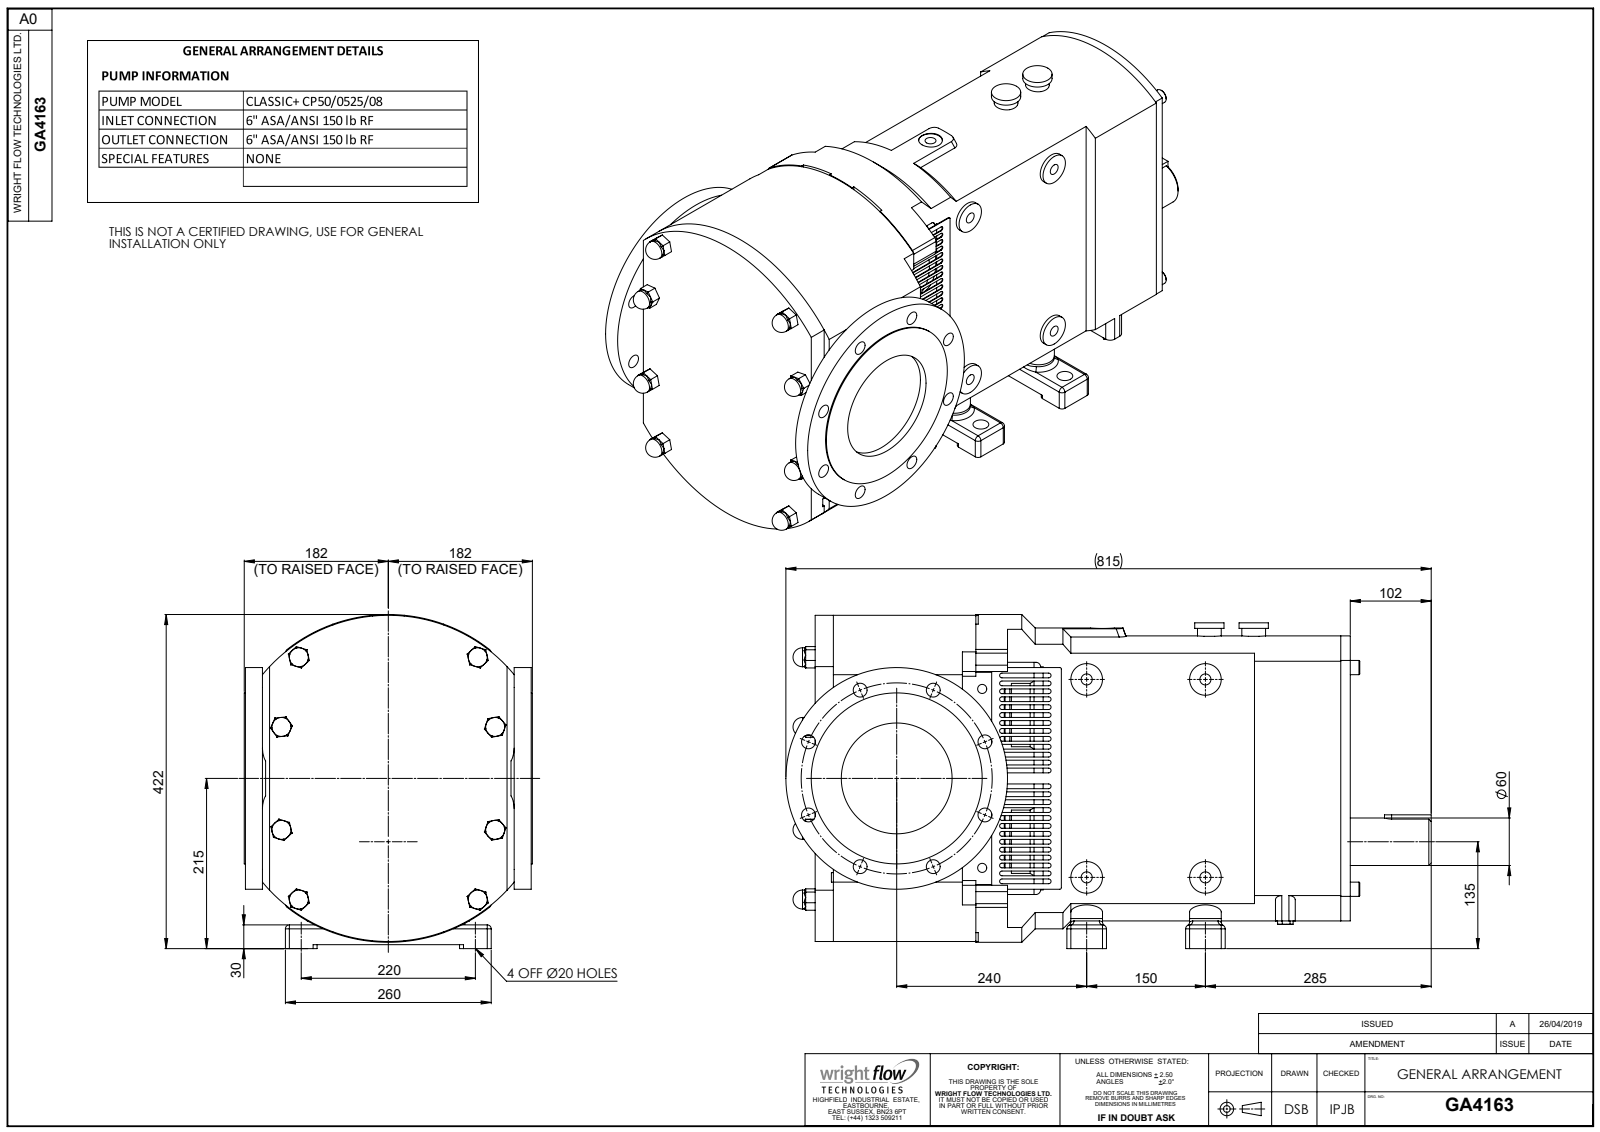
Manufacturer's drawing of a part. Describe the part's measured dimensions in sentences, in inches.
The part is named "Copy of CP50L-0525 ASA150 H BSD^GA4163; GA4163". Its 3-D file was written by "SolidWorks 2023 (AUTOMOTIVE_DESIGN)". It is 1 solid with 1197 faces: 521 planar, 414 cylindrical and 262 other. Overall it measures 32.096 by 16.614 by 14.331 inches. Its volume is 3 295 cubic inches and its surface area 2 341 square inches. Round holes: 8 of diameter 0.689, 4 of diameter 0.551, 4 of diameter 0.787, 2 of diameter 0.453, 2 of diameter 1.378, 1 of diameter 0.545, 1 of diameter 1.181, 1 of diameter 5.512. Round bosses or shafts: 8 of diameter 1.575, 8 of diameter 0.945, 4 of diameter 0.709, 2 of diameter 6.654, 2 of diameter 3.15, 2 of diameter 2.756, 2 of diameter 2.677, 2 of diameter 1.457. Partial cylindrical surfaces (rounded edges, fillets, slot ends): 52 of radius 0.118, 36 of radius 0.197, 22 of radius 0.236, 12 of radius 0.315, 4 of radius 0.079, 1 of radius 0.354, 1 of radius 6.083, 1 of radius 6.496. The main face-to-face distances are 6.772, 7.421, 0.65, 26.614, 7.323, 19.291, 3.071, 3.72, 10.492, 11.142. The hole center spacings are 4.75, 6.718, 8.777, 3.635, 3.636, 5.906, 9.5, 2.435.
